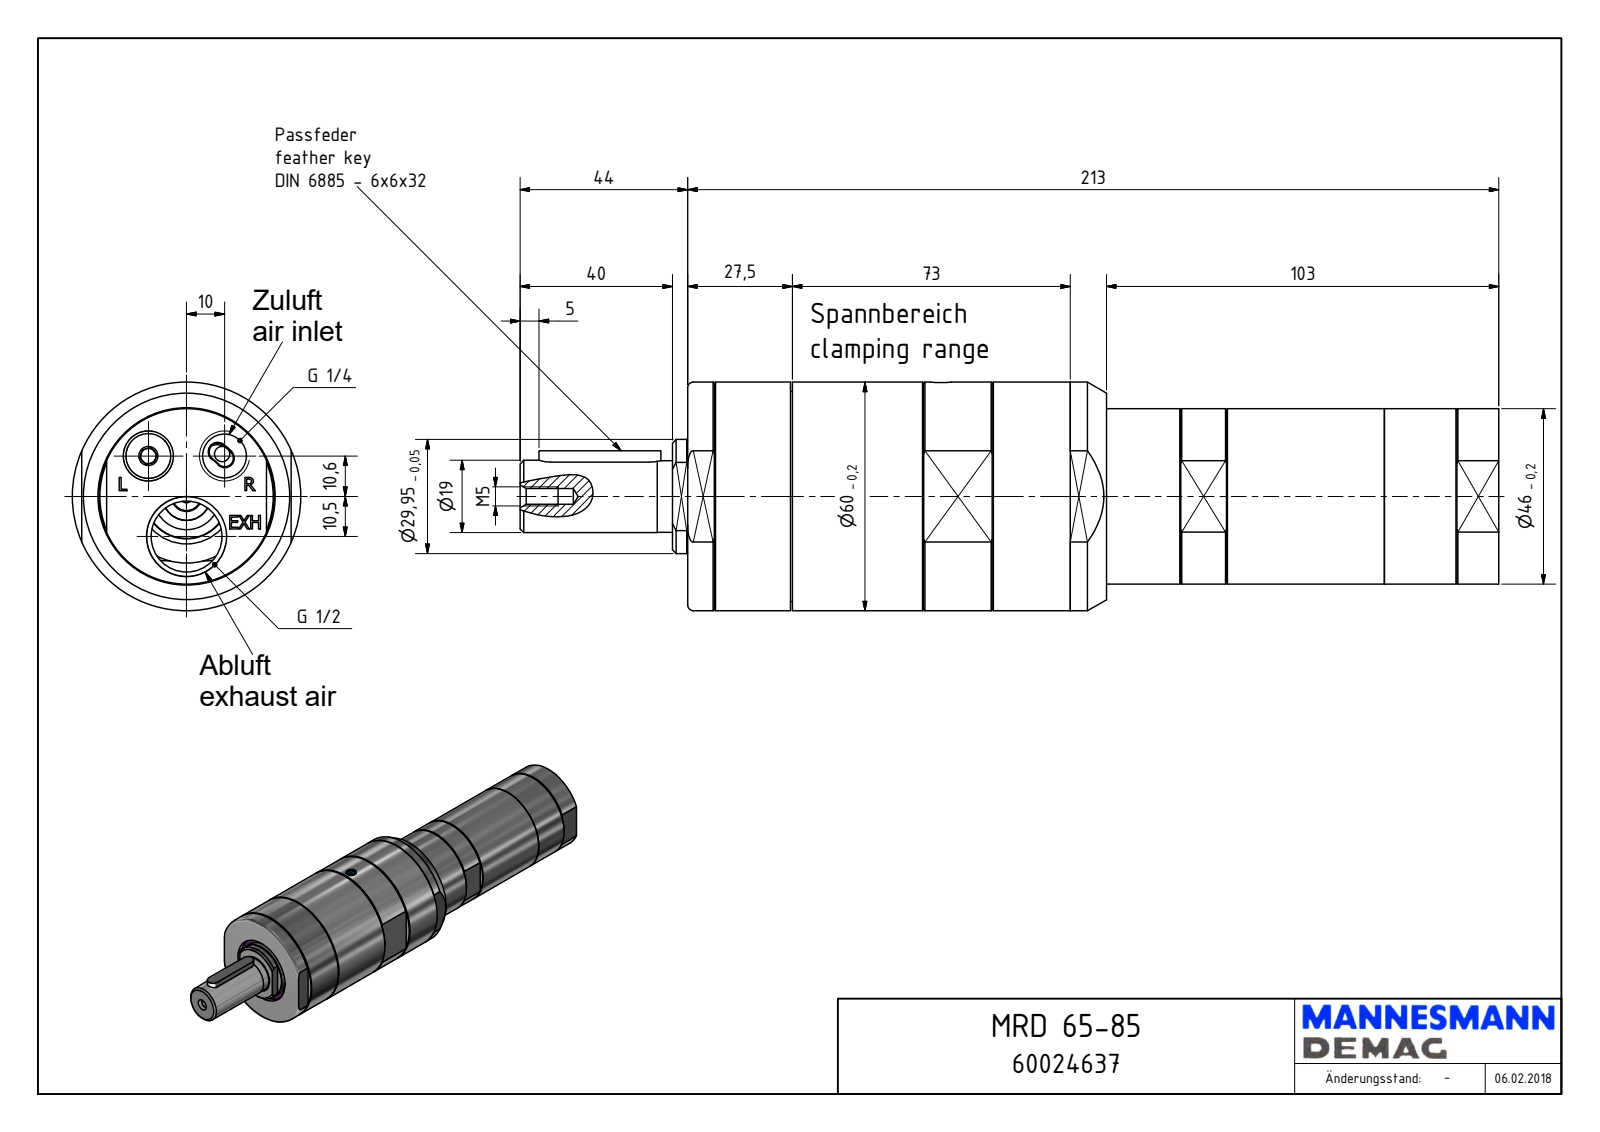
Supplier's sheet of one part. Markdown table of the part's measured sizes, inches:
| quantity | value |
| --- | --- |
| part name | MRD 65-85_60024637 |
| STEP written by | Autodesk Inventor 2018 (AUTOMOTIVE_DESIGN) |
| units | inches |
| bodies | 1 solid, 230 faces (129 planar, 52 cylindrical, 49 other) |
| overall size | 10.118 × 2.362 × 2.362 |
| volume | 29.66 in³ |
| surface area | 75.62 in² |
| round holes (diameter × count) | 0.157 × 2, 0.061 × 1, 0.163 × 1, 0.217 × 1, 0.451 × 1, 0.733 × 1, 1.378 × 1, 1.831 × 1, 2.18 × 1 |
| round bosses / shafts (diameter × count) | 2.362 × 1, 2.172 × 1, 1.811 × 1, 1.285 × 1, 1.179 × 1, 0.748 × 1, 0.74 × 1, 0.197 × 1 |
| partial cylindrical surfaces (radius × count) | 0.098 × 4, 0.118 × 2, 0.197 × 2, 0.225 × 1, 0.659 × 1, 0.748 × 1, 1.045 × 1 |
| main face-to-face distances | 8.386, 0.256, 1.909, 2.165, 4.055, 4.331, 7.303, 1.083, 3.248, 1.654 |
| hole center spacings | 0.574, 0.919, 0.413, 0.787 |
